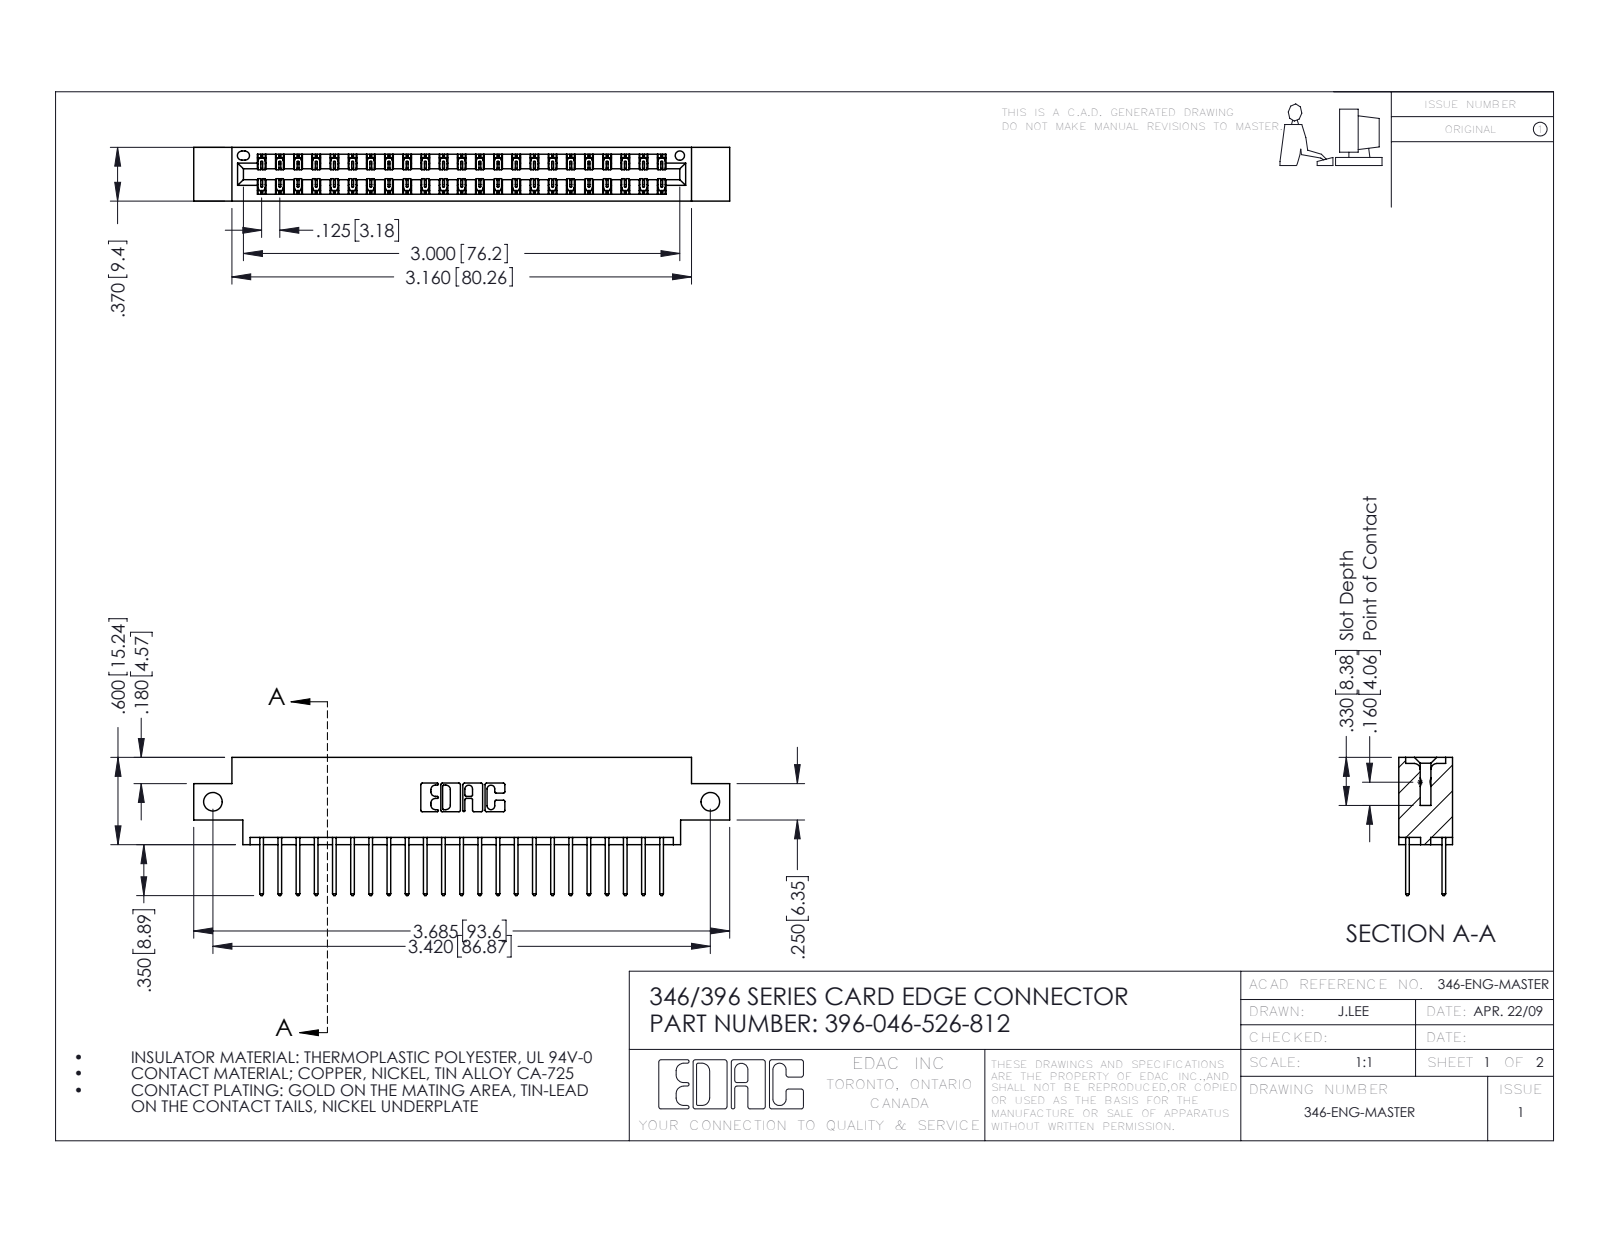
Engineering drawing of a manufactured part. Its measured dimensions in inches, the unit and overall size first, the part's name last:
Units: inches
Overall size (bounding box): 3.685 × 0.95 × 0.37
Round holes (diameter × count): ⌀0.128 ×2, ⌀0.064 ×1
Partial cylindrical surfaces — rounded edges, fillets, slot ends (radius × count): R0.006 ×69, R0.01 ×46, R0.01 ×22, R0.007 ×6, R0.031 ×6, R0.026 ×3, R0.014 ×2, R0.022 ×2
Main face-to-face distances: 0.048, 0.322, 0.25, 0.37, 0.072, 0.298, 0.025, 0.275, 0.148, 0.222
Hole centre spacings: 3.42
Volume: 0.538 in³ · Surface area: 18.9 in²
Bodies: 47 solids, 2518 faces (1690 planar, 828 cylindrical, 0 other)
Part name (STEP PRODUCT): 396-046-526-812; 346 Part_0.170 Offset - Side Mount; 345-292-001_345-293-126
STEP written by: SolidWorks 2016 (CONFIG_CONTROL_DESIGN)
